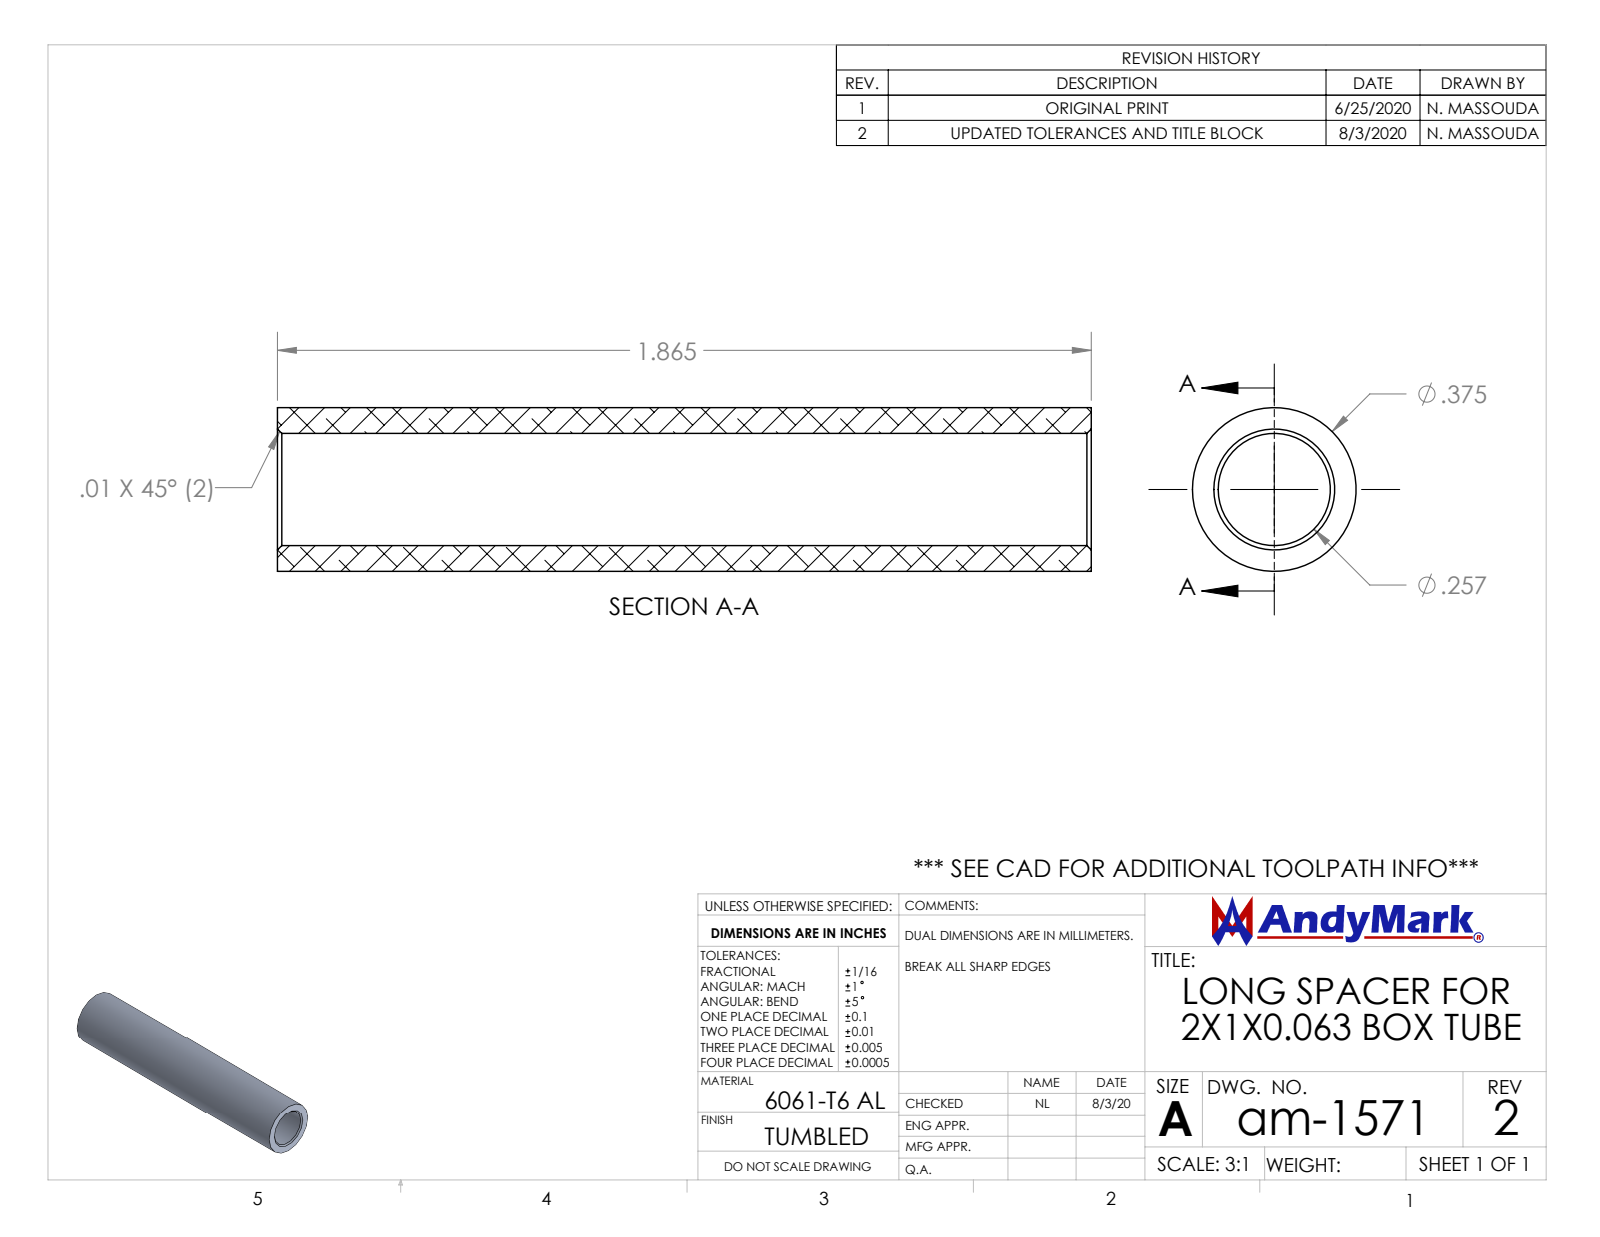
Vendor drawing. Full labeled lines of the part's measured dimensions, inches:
Part name (STEP PRODUCT): am-1571 0.375 OD x 0.257 ID x 1.865 Long Aluminum Spacer for Box Tube
STEP written by: SolidWorks 2019 (CONFIG_CONTROL_DESIGN)
Units: inches
Bodies: 1 solid, 10 faces (2 planar, 4 cylindrical, 4 other)
Overall size (bounding box): 1.865 × 0.375 × 0.375
Volume: 0.109 in³ · Surface area: 3.811 in²
Round holes (diameter × count): ⌀0.257 ×1
Round bosses / shafts (diameter × count): ⌀0.375 ×1
Main face-to-face distances: 1.865
